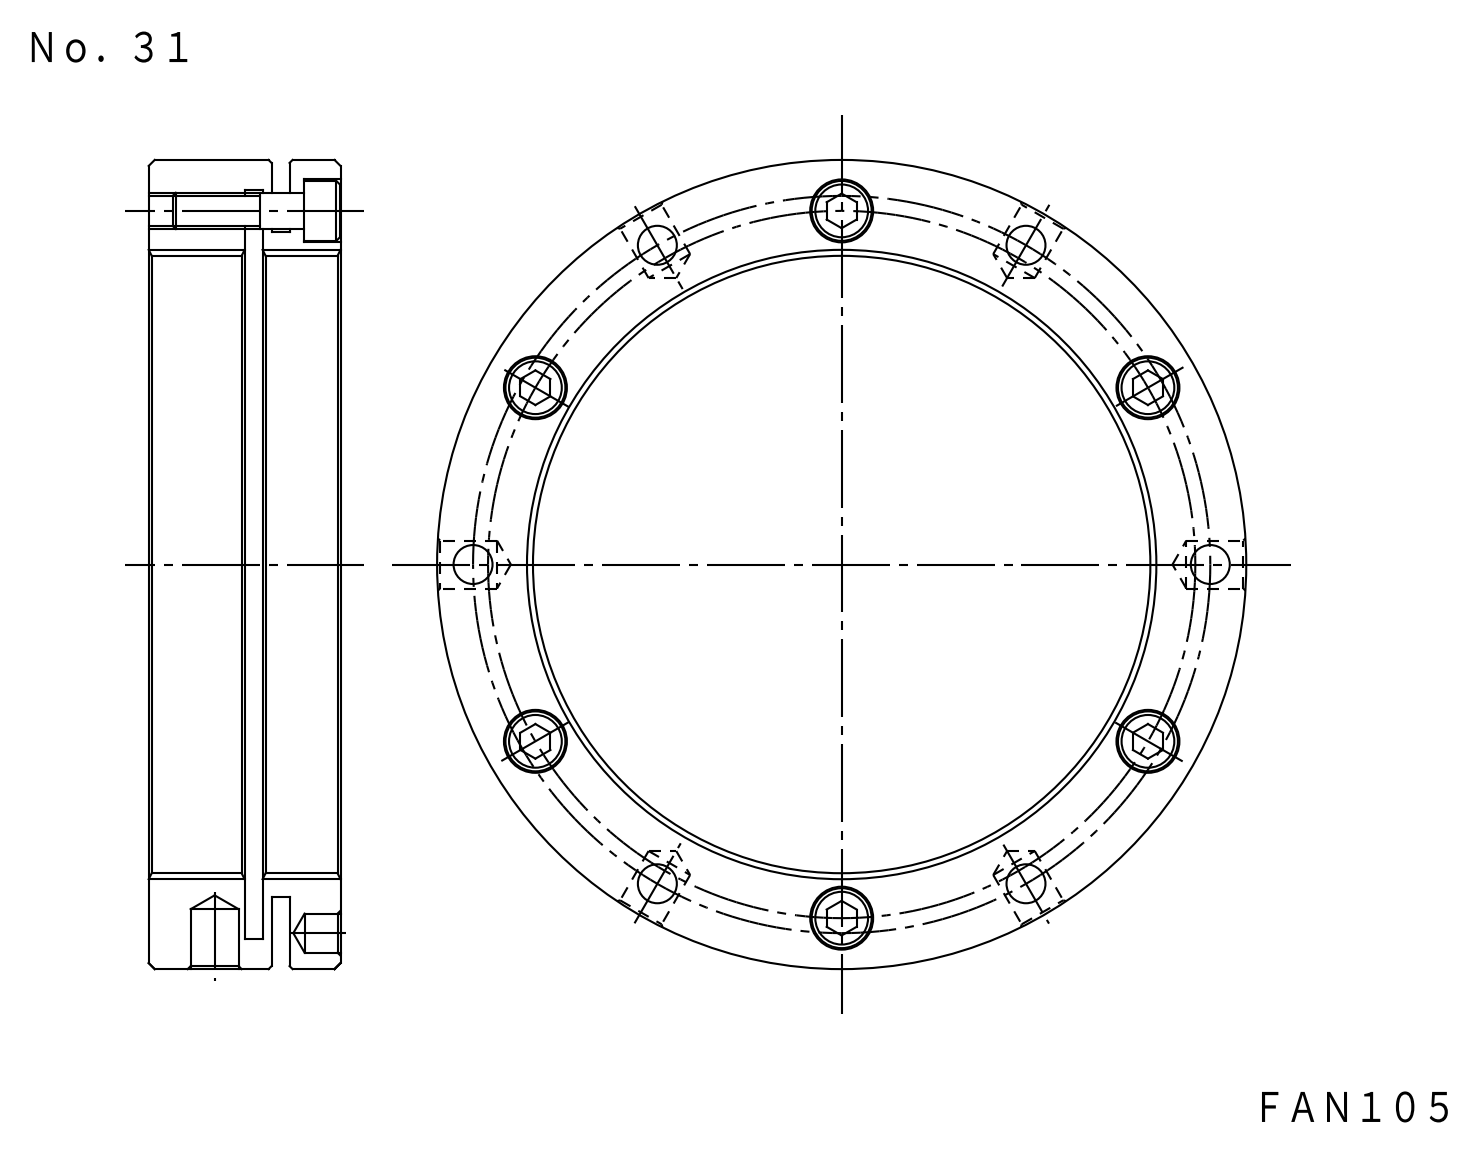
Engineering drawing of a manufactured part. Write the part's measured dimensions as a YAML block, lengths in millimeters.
part_name: "FKD FAN105; M6X22_default"
step_written_by: "SolidWorks 2012 (CONFIG_CONTROL_DESIGN)"
units: millimeters
bodies: {solids: 7, faces: 204, planar: 72, cylindrical: 108, other: 24}
overall_size: [135, 135, 32]
volume: 156662
surface_area: 61126
round_holes:
  - {diameter: 6.3, count: 6}
  - {diameter: 6.5, count: 6}
  - {diameter: 10.5, count: 6}
  - {diameter: 4.92, count: 4}
  - {diameter: 8, count: 3}
  - {diameter: 4.92, count: 2}
  - {diameter: 105, count: 1}
  - {diameter: 128, count: 1}
round_bosses_or_shafts:
  - {diameter: 10, count: 6}
  - {diameter: 6, count: 6}
  - {diameter: 135, count: 1}
  - {diameter: 114, count: 1}
face_to_face_distances: [2.5, 4, 32, 17, 15, 19.5, 12.5, 21, 1.5, 11]
hole_center_spacings: [31.59, 60.5, 61.5, 86.27, 117.84, 106.52, 104.79, 123]
